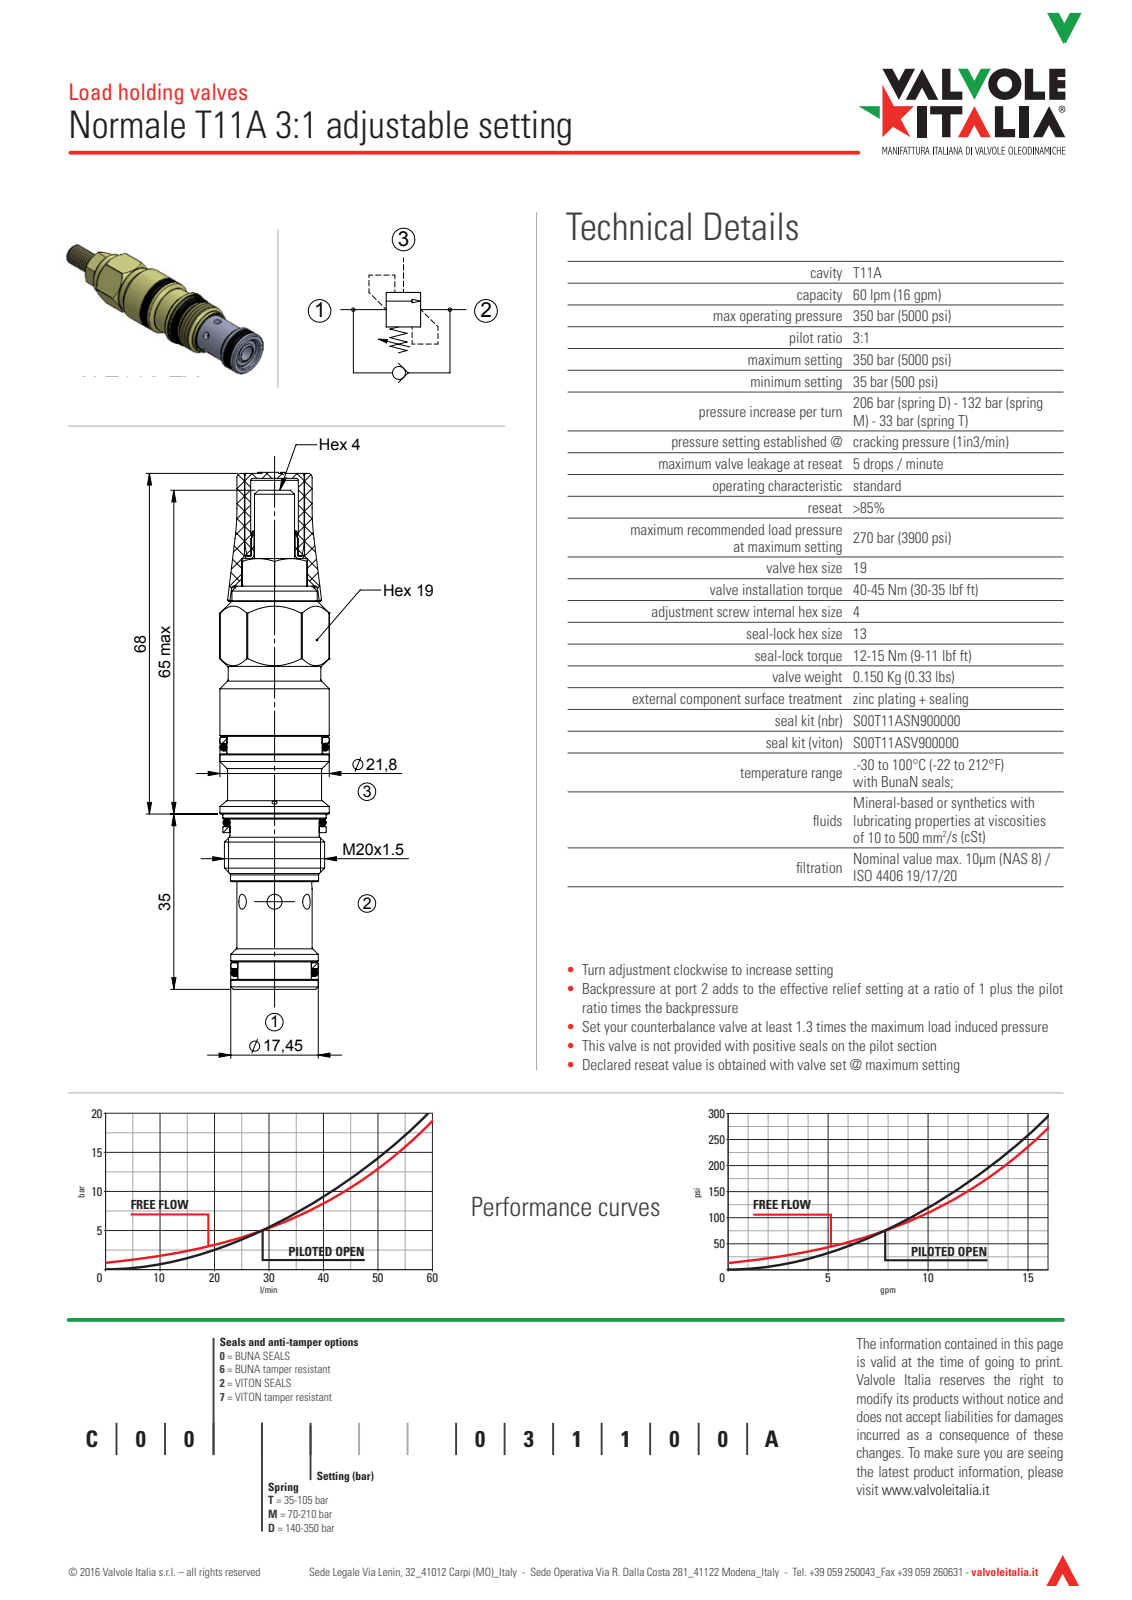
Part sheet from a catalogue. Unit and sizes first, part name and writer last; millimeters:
Units: millimetres
Overall size (bounding box): 94.84 × 21.8 × 21.8
Round holes (diameter × count): ⌀3 ×3, ⌀1 ×1, ⌀2 ×1, ⌀6.2 ×1, ⌀8.2 ×1, ⌀12.5 ×1, ⌀16 ×1
Round bosses / shafts (diameter × count): ⌀21.8 ×1, ⌀20.6 ×1, ⌀20.3 ×1, ⌀20 ×1, ⌀18.8 ×1, ⌀18.5 ×1, ⌀17.8 ×1, ⌀17.6 ×1
Partial cylindrical surfaces — rounded edges, fillets, slot ends (radius × count): R2 ×1, R7.5 ×1, R10.75 ×1
Main face-to-face distances: 19, 13, 45, 28.7, 8.5, 43.5, 32, 3.5, 3.3, 2
Bodies: 0 solids, 218 faces (44 planar, 76 cylindrical, 98 other)
Part name (STEP PRODUCT): C000D210031100A
STEP written by: SolidWorks 2015 (AUTOMOTIVE_DESIGN)
